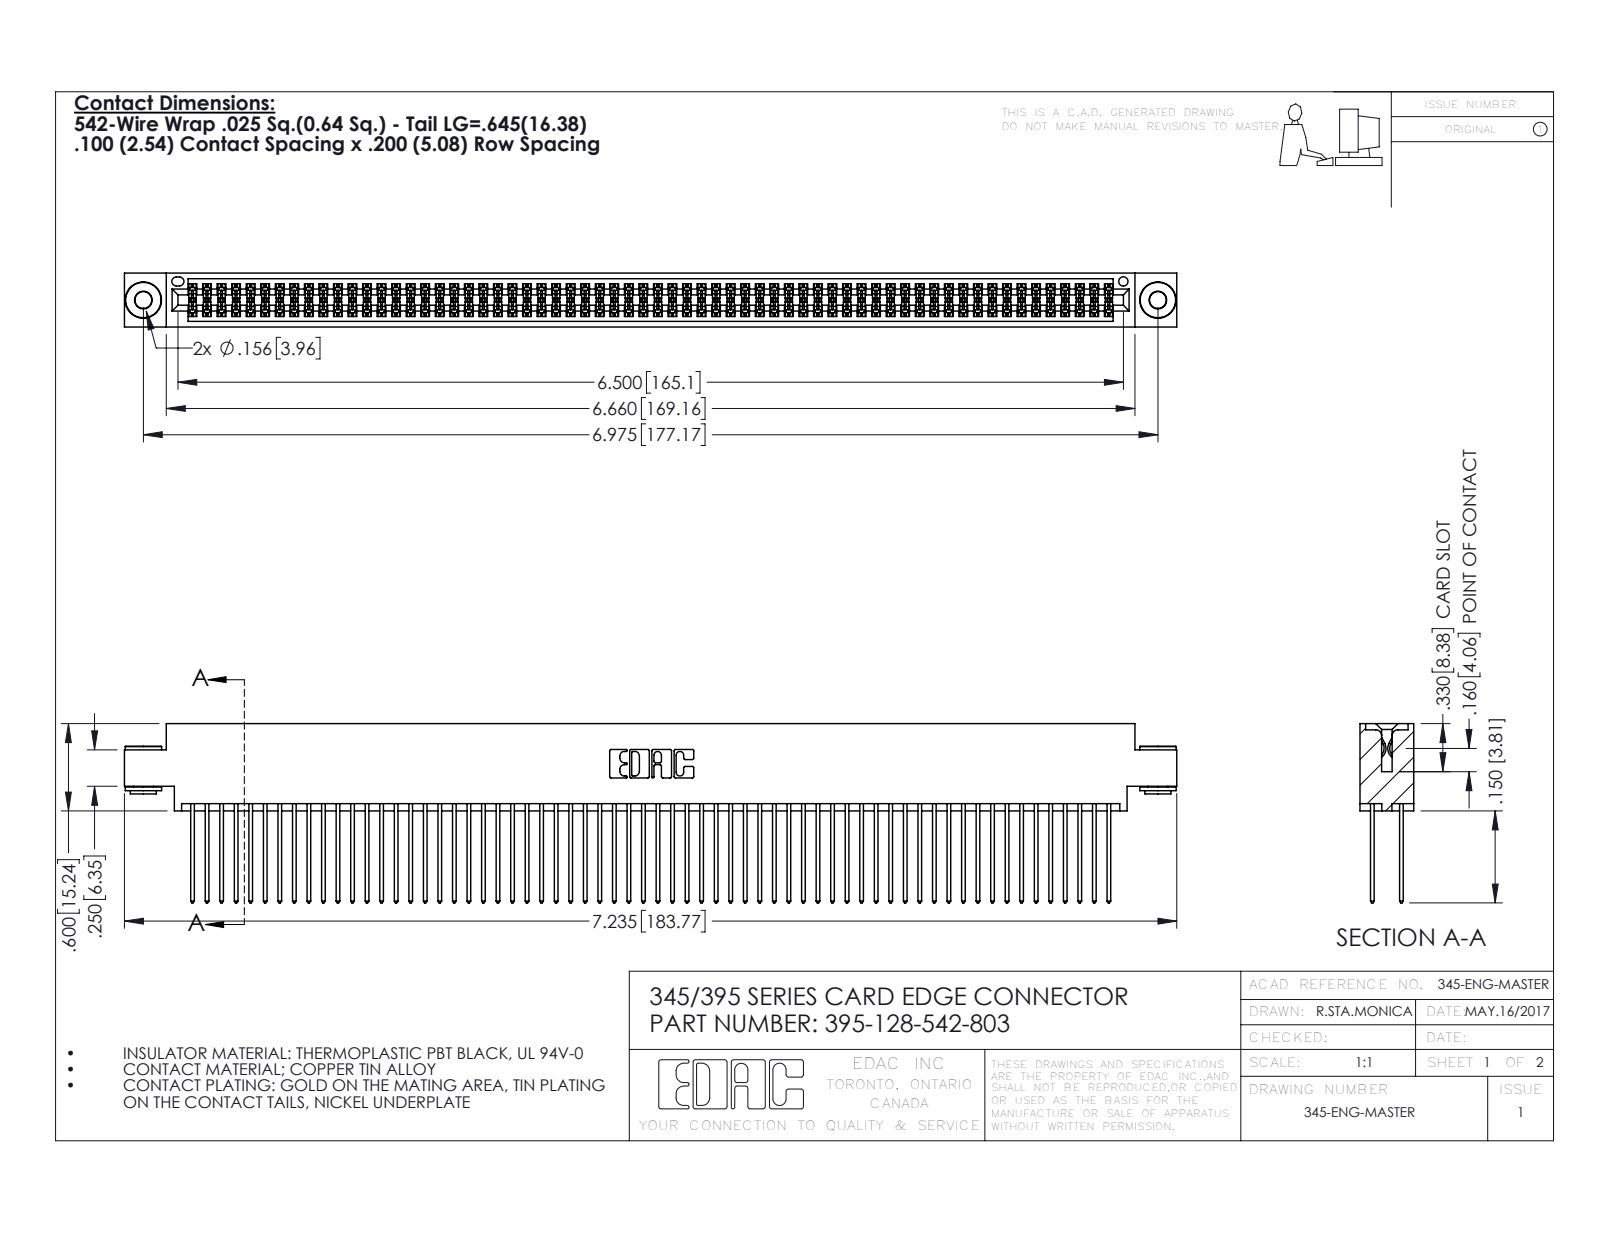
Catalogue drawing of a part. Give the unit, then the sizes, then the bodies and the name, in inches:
Units: inches
Overall size (bounding box): 7.235 × 1.232 × 0.37
Round holes (diameter × count): ⌀0.116 ×2, ⌀0.156 ×2, ⌀0.064 ×1
Round bosses / shafts (diameter × count): ⌀0.25 ×2, ⌀0.18 ×2, ⌀0.136 ×2
Partial cylindrical surfaces — rounded edges, fillets, slot ends (radius × count): R0.006 ×192, R0.01 ×128, R0.01 ×22, R0.007 ×6, R0.031 ×6, R0.026 ×3, R0.014 ×2, R0.019 ×2
Main face-to-face distances: 0.072, 0.298, 0.2, 0.098, 0.272, 0.025, 0.37, 0.225, 0.175, 0.149
Hole centre spacings: 0.27, 6.739, 6.975
Volume: 1.133 in³ · Surface area: 48.04 in²
Bodies: 131 solids, 6568 faces (4318 planar, 2242 cylindrical, 8 other)
Part name (STEP PRODUCT): 345-292-001_345-293-142; 345 Part_0.170 Offset - 0.156 Dia-TH; 395-128-542-803; 345-250-002_345-250-002-102
STEP written by: SolidWorks 2016 (CONFIG_CONTROL_DESIGN)
